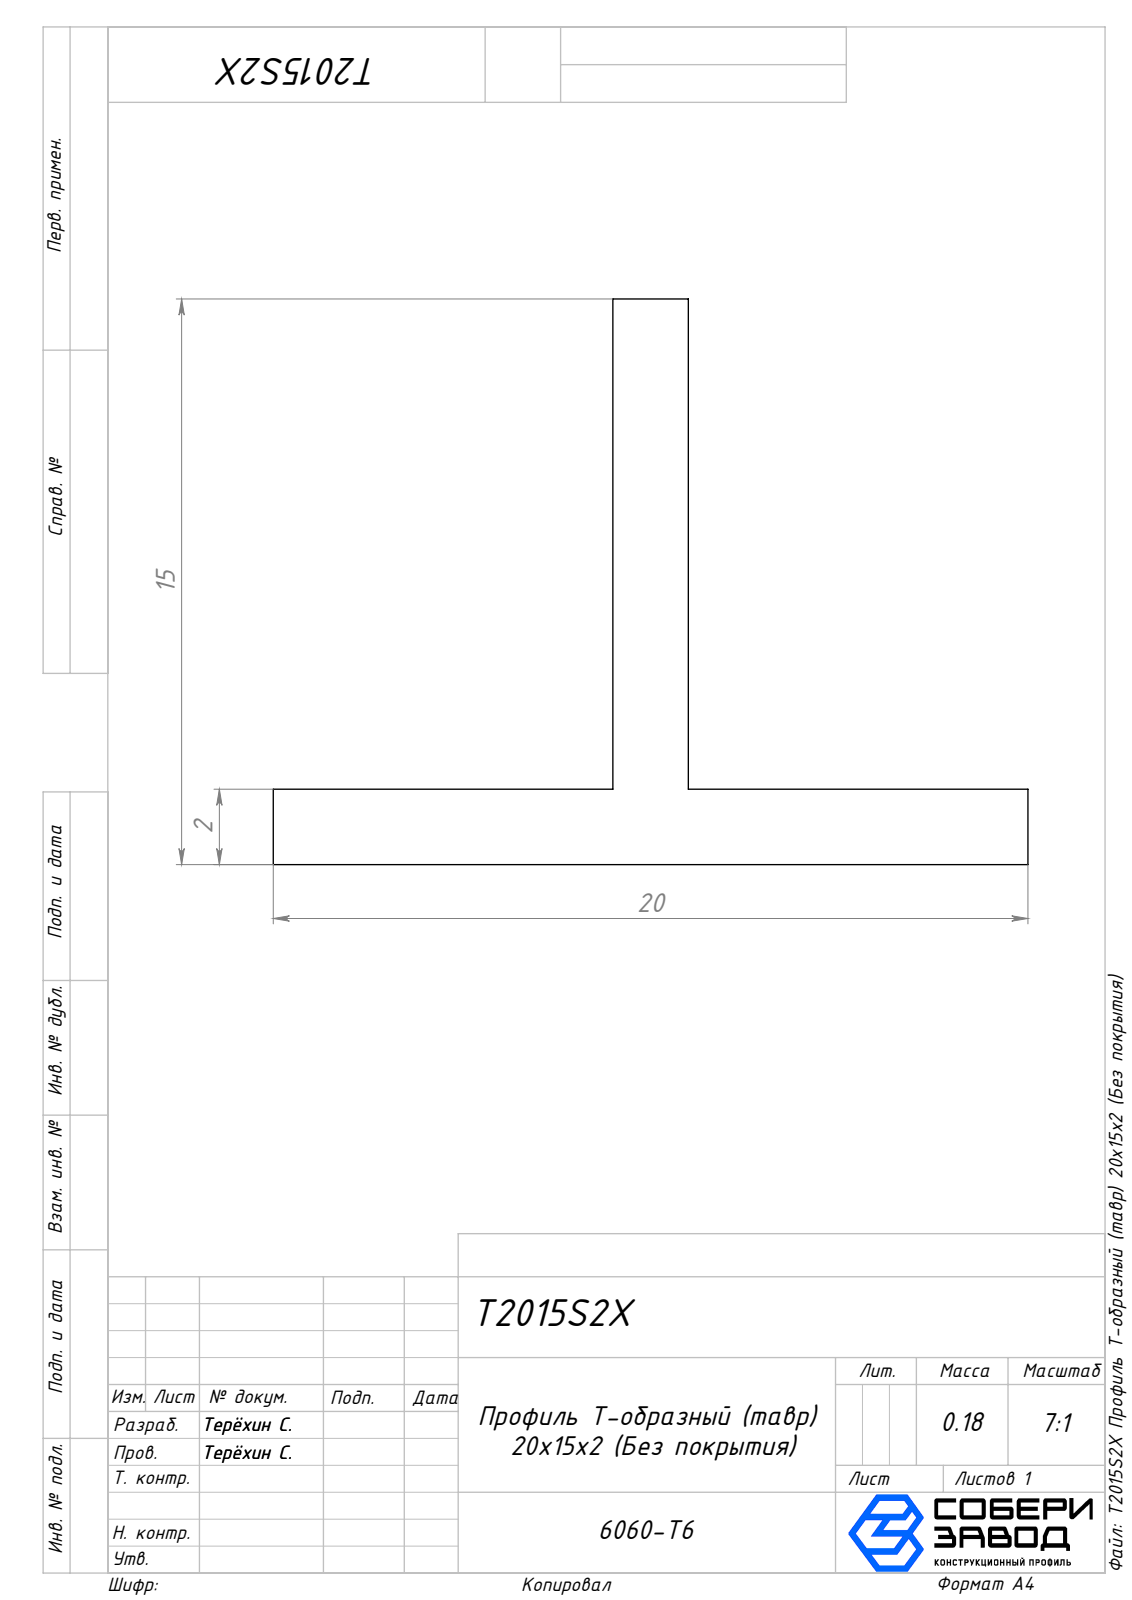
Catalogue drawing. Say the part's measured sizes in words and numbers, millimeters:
The part is named "T2015S2X Профиль Т-образный (тавр) 20х15х2 (Без покрытия)_00; Сборка1". Its 3-D file was written by "SolidWorks 2025 (AUTOMOTIVE_DESIGN)". It is 1 solid with 10 faces: 10 planar, 0 cylindrical and 0 other. Overall it measures 1000 by 20 by 15 millimeters. Its volume is 66 000 cubic millimeters and its surface area 70 132 square millimeters. The main face-to-face distances are 2, 9, 11, 20, 15, 13, 1000.
